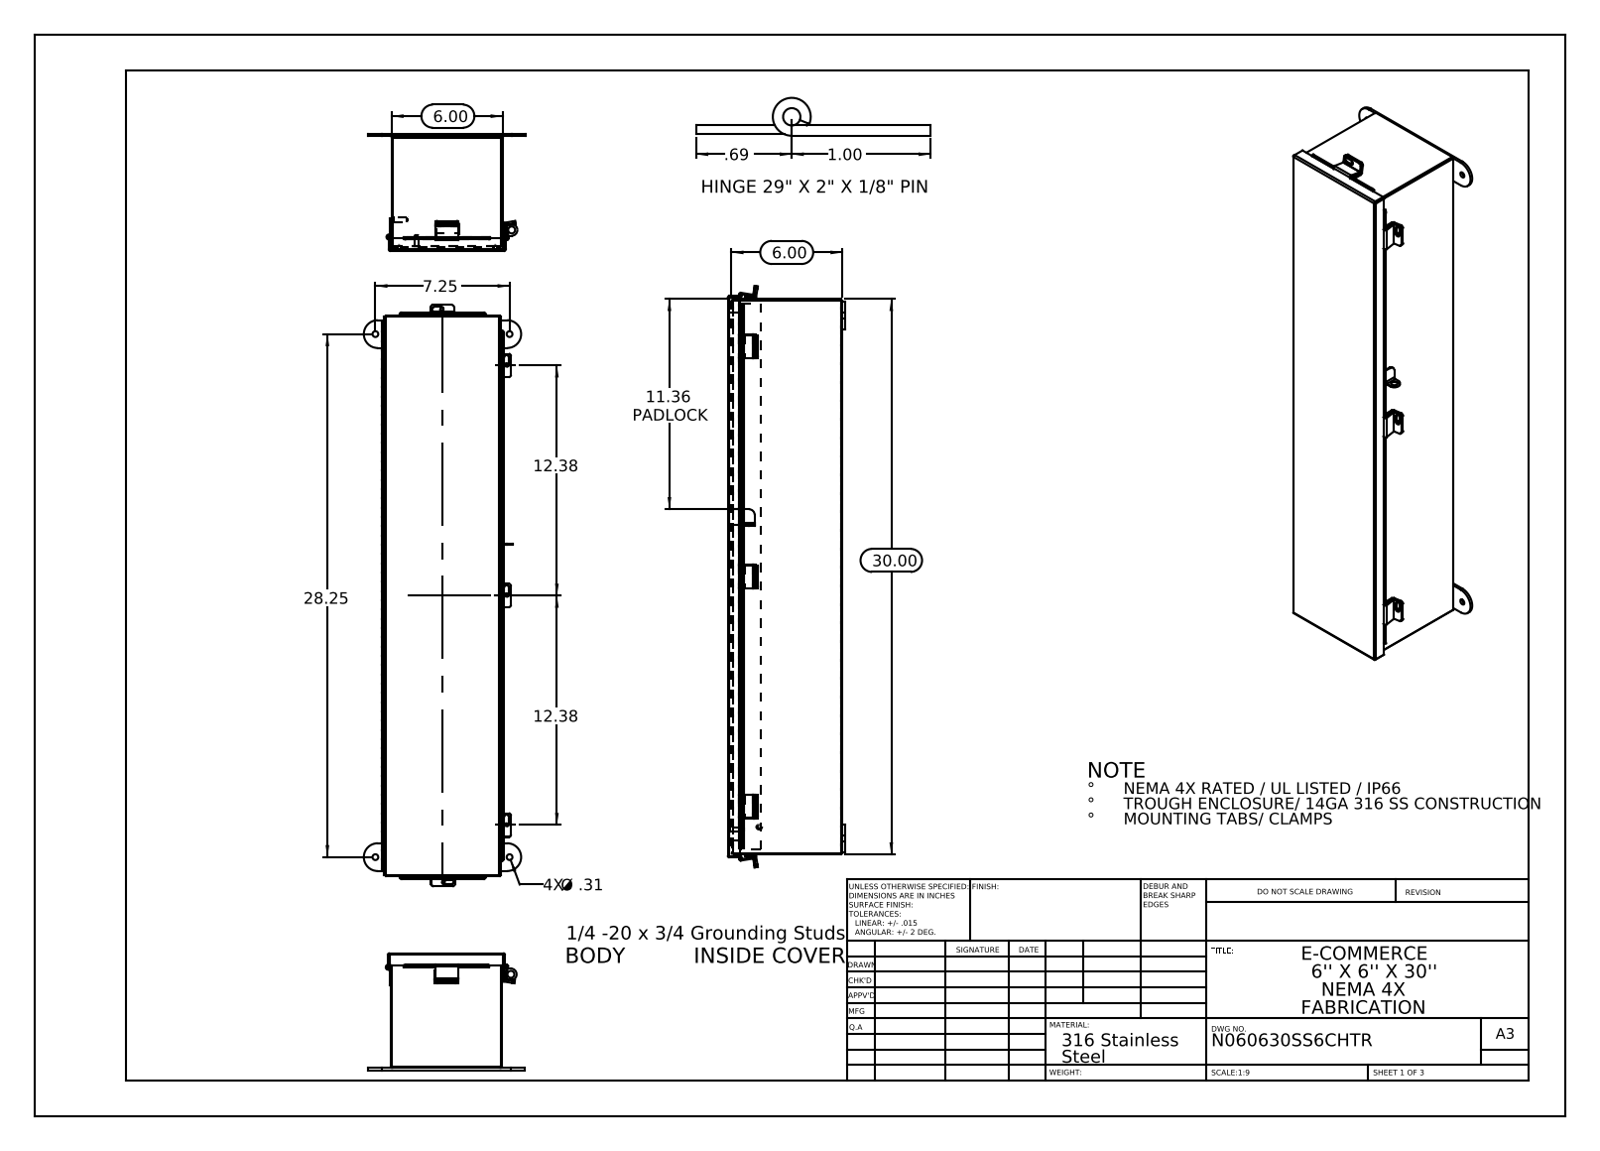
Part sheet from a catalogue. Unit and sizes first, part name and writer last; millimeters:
Units: millimetres
Overall size (bounding box): 797.7 × 215.9 × 161
Round holes (diameter × count): ⌀6.4 ×5, ⌀8 ×4, ⌀3.2 ×1, ⌀9.5 ×1
Round bosses / shafts (diameter × count): ⌀8 ×2, ⌀6 ×2, ⌀6.9 ×1, ⌀6.4 ×1
Partial cylindrical surfaces — rounded edges, fillets, slot ends (radius × count): R3.2 ×17, R0.2 ×12, R0.3 ×10, R2.2 ×10, R3.4 ×10, R2.1 ×6, R2.5 ×6, R19.1 ×4
Main face-to-face distances: 1.9, 150.5, 155.7, 152.4, 148.6, 157.6, 153.7, 3.8, 154.3, 760.1
Hole centre spacings: 184.2, 315.6, 717.6, 740.8, 168.6, 631.2
Volume: 1 198 000 mm³ · Surface area: 1 267 000 mm²
Bodies: 21 solids, 1006 faces (613 planar, 373 cylindrical, 20 other)
Part name (STEP PRODUCT): HW-CLH-JH-20154; N060630SSCHTR JIC Top; N060630SSCHTR JIC Bottom; N060630SSCHTR HW-CD-S-25020-034 (+8 more)
STEP written by: SolidWorks 2013 (CONFIG_CONTROL_DESIGN)
